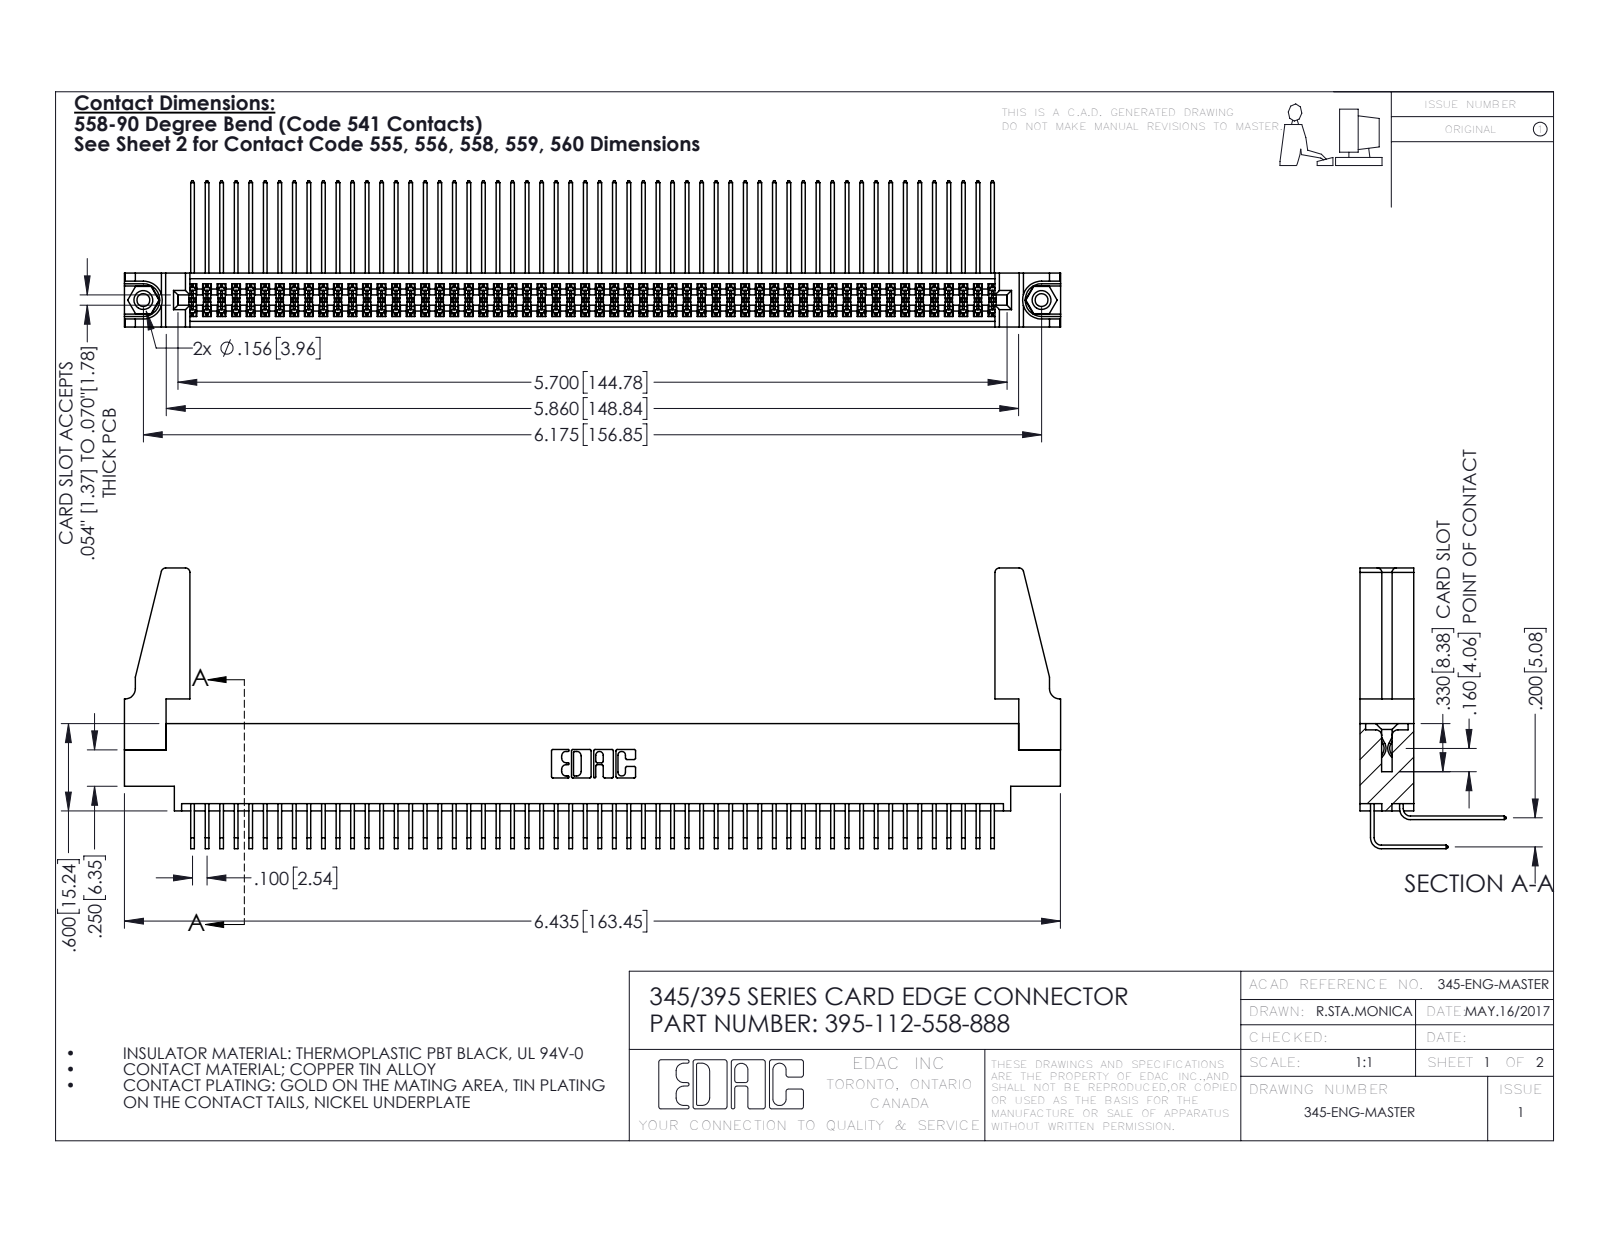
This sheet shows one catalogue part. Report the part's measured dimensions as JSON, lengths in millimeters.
{"part_name": "345-250-001_345-250-001-102; 345-292-001_558 559 Tail - 1; 345 Part_0.170 Offset - 0.156 Dia-TH; 345-220-078_345-220-088 (+2 more)", "step_written_by": "SolidWorks 2016 (CONFIG_CONTROL_DESIGN)", "units": "millimeters", "bodies": {"solids": 117, "faces": 6078, "planar": 4076, "cylindrical": 1986, "other": 16}, "overall_size": [163.5, 49, 25.5], "volume_mm3": 19800, "surface_area_mm2": 31030, "round_holes": [[2.3, 2], [3.2, 2], [4, 2], [1.6, 1]], "round_bosses_or_shafts": [[3.9, 2]], "partial_cylinders_radius": [[0.2, 169], [0.3, 22], [0.8, 8], [0.2, 6], [0.8, 6], [0.7, 3], [0.4, 2], [0.5, 2]], "face_to_face_distances": [1.8, 7.6, 5.1, 9.4, 2.5, 6.9, 0.6, 5.7, 4.4, 0.6], "hole_center_spacings": [6.9, 150.9, 156.8]}
